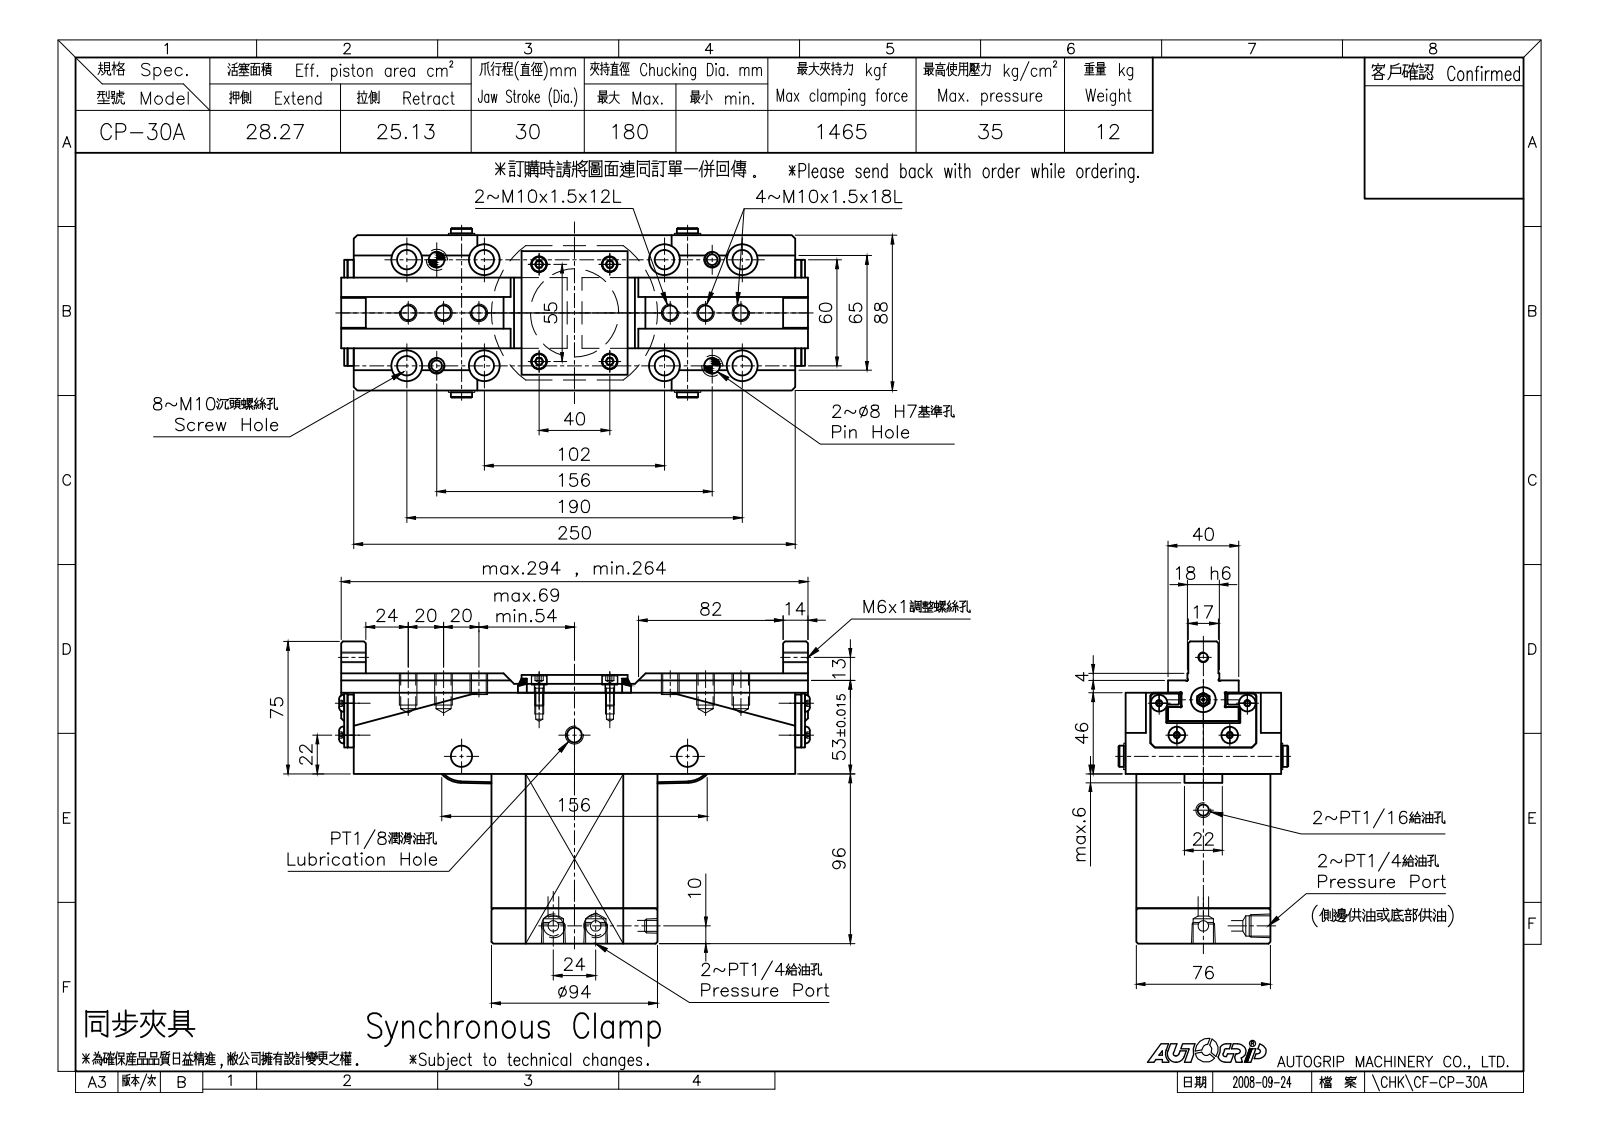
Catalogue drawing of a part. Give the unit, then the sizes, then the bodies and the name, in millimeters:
Units: millimetres
Overall size (bounding box): 289.94 × 171 × 88
Round holes (diameter × count): ⌀9 ×8, ⌀11 ×8, ⌀17.5 ×8, ⌀8.5 ×6, ⌀10 ×6, ⌀6 ×5, ⌀4.2 ×4, ⌀5 ×4, ⌀5.5 ×4, ⌀11.5 ×4, ⌀6.3 ×2, ⌀8 ×2
Round bosses / shafts (diameter × count): ⌀8.5 ×4
Partial cylindrical surfaces — rounded edges, fillets, slot ends (radius × count): R5 ×4, R4 ×2, R6 ×2, R15 ×2, R53.5 ×2, R47 ×1
Main face-to-face distances: 24, 64, 30, 76, 6, 106, 18, 40, 82, 58
Hole centre spacings: 91.21, 60, 17, 20, 27, 28.64, 31.06, 31.1
Volume: 1 562 000 mm³ · Surface area: 226 269 mm²
Bodies: 12 solids, 699 faces (394 planar, 180 cylindrical, 125 other)
Part name (STEP PRODUCT): CP-30A外觀參考; CP-30後蓋簡易; CP-30缸體簡易; M5x12 (+4 more)
STEP written by: SolidWorks 2011 (AUTOMOTIVE_DESIGN)
